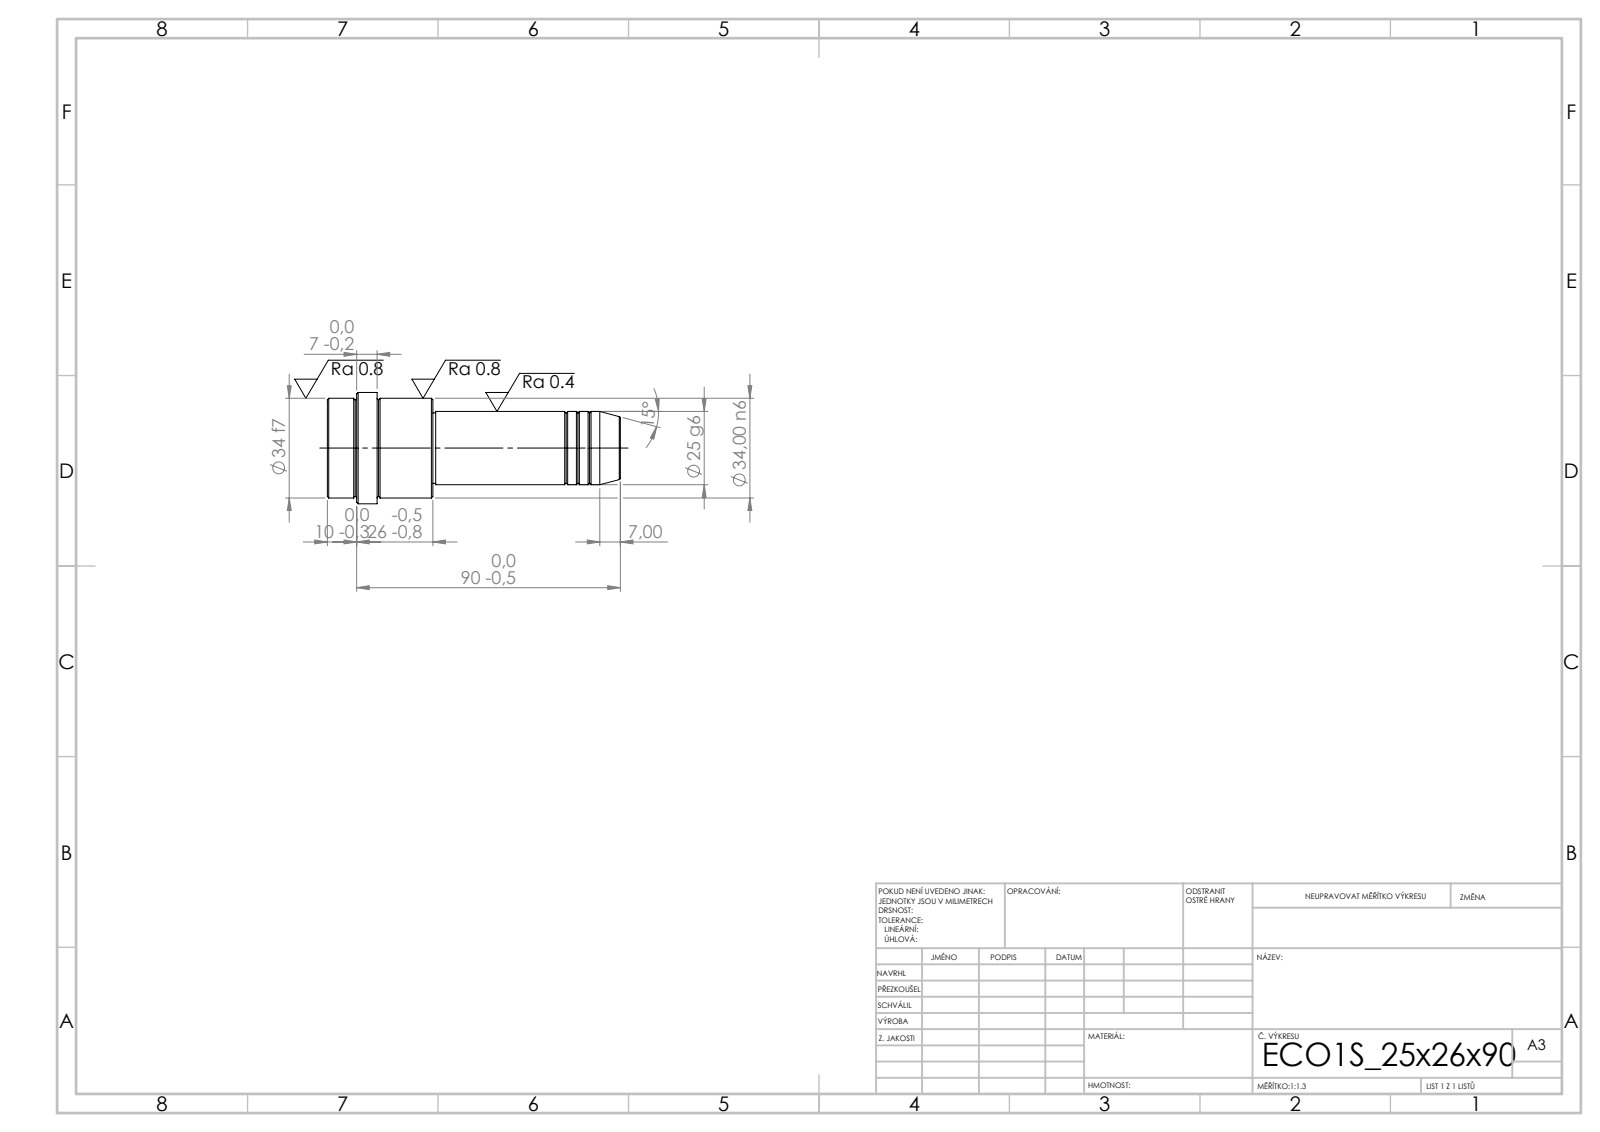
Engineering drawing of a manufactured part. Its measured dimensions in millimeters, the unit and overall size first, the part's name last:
Units: millimetres
Overall size (bounding box): 100 × 38 × 38
Round bosses / shafts (diameter × count): ⌀38 ×1, ⌀34 ×1, ⌀25 ×1, ⌀24 ×1
Main face-to-face distances: 36, 64, 100, 83, 19, 17, 90, 26, 7, 10
Volume: 64 939 mm³ · Surface area: 11 277 mm²
Bodies: 1 solid, 52 faces (6 planar, 16 cylindrical, 30 other)
STEP written by: SolidWorks 2019 (CONFIG_CONTROL_DESIGN)
